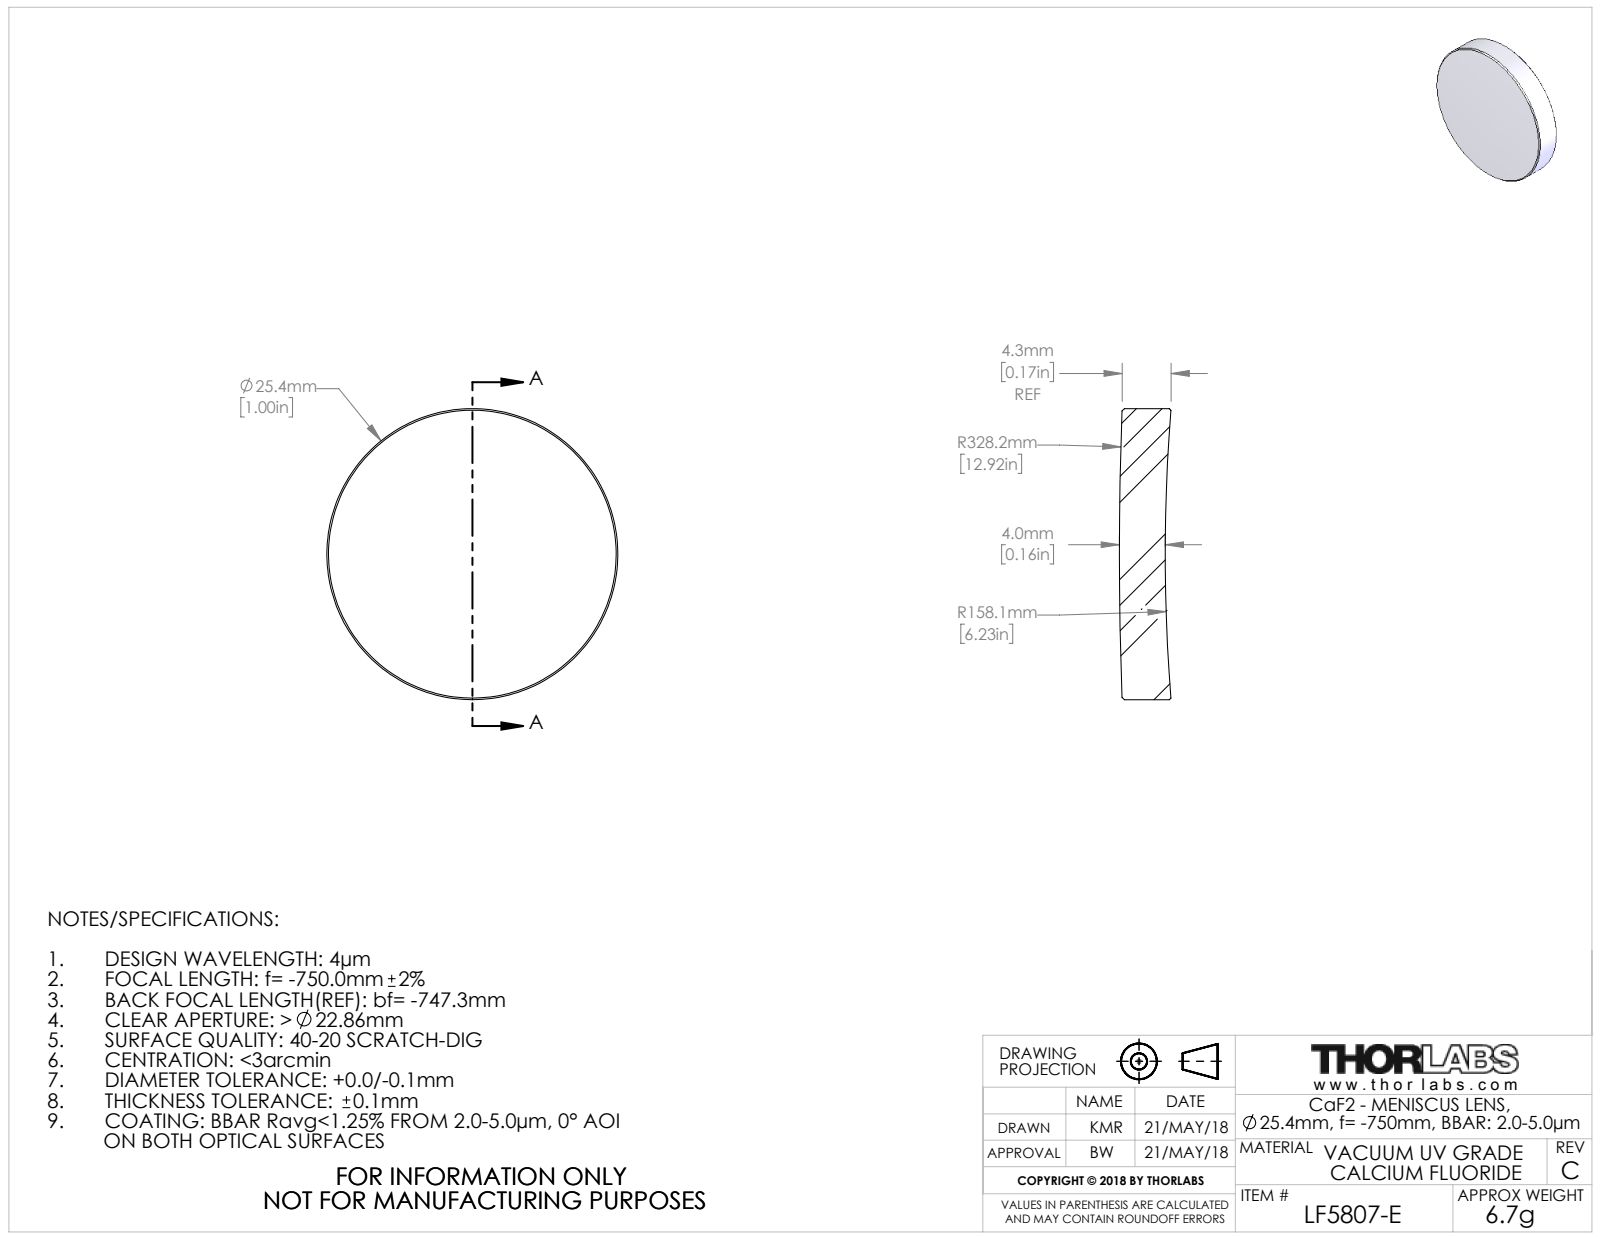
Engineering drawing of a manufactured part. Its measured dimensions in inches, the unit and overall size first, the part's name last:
Units: inches
Overall size (bounding box): 1 × 1 × 0.177
Round bosses / shafts (diameter × count): ⌀1 ×1
Volume: 0.128 in³ · Surface area: 2.074 in²
Bodies: 1 solid, 10 faces (0 planar, 2 cylindrical, 8 other)
Part name (STEP PRODUCT): 20179-E0W
STEP written by: SolidWorks 2016 (CONFIG_CONTROL_DESIGN)
